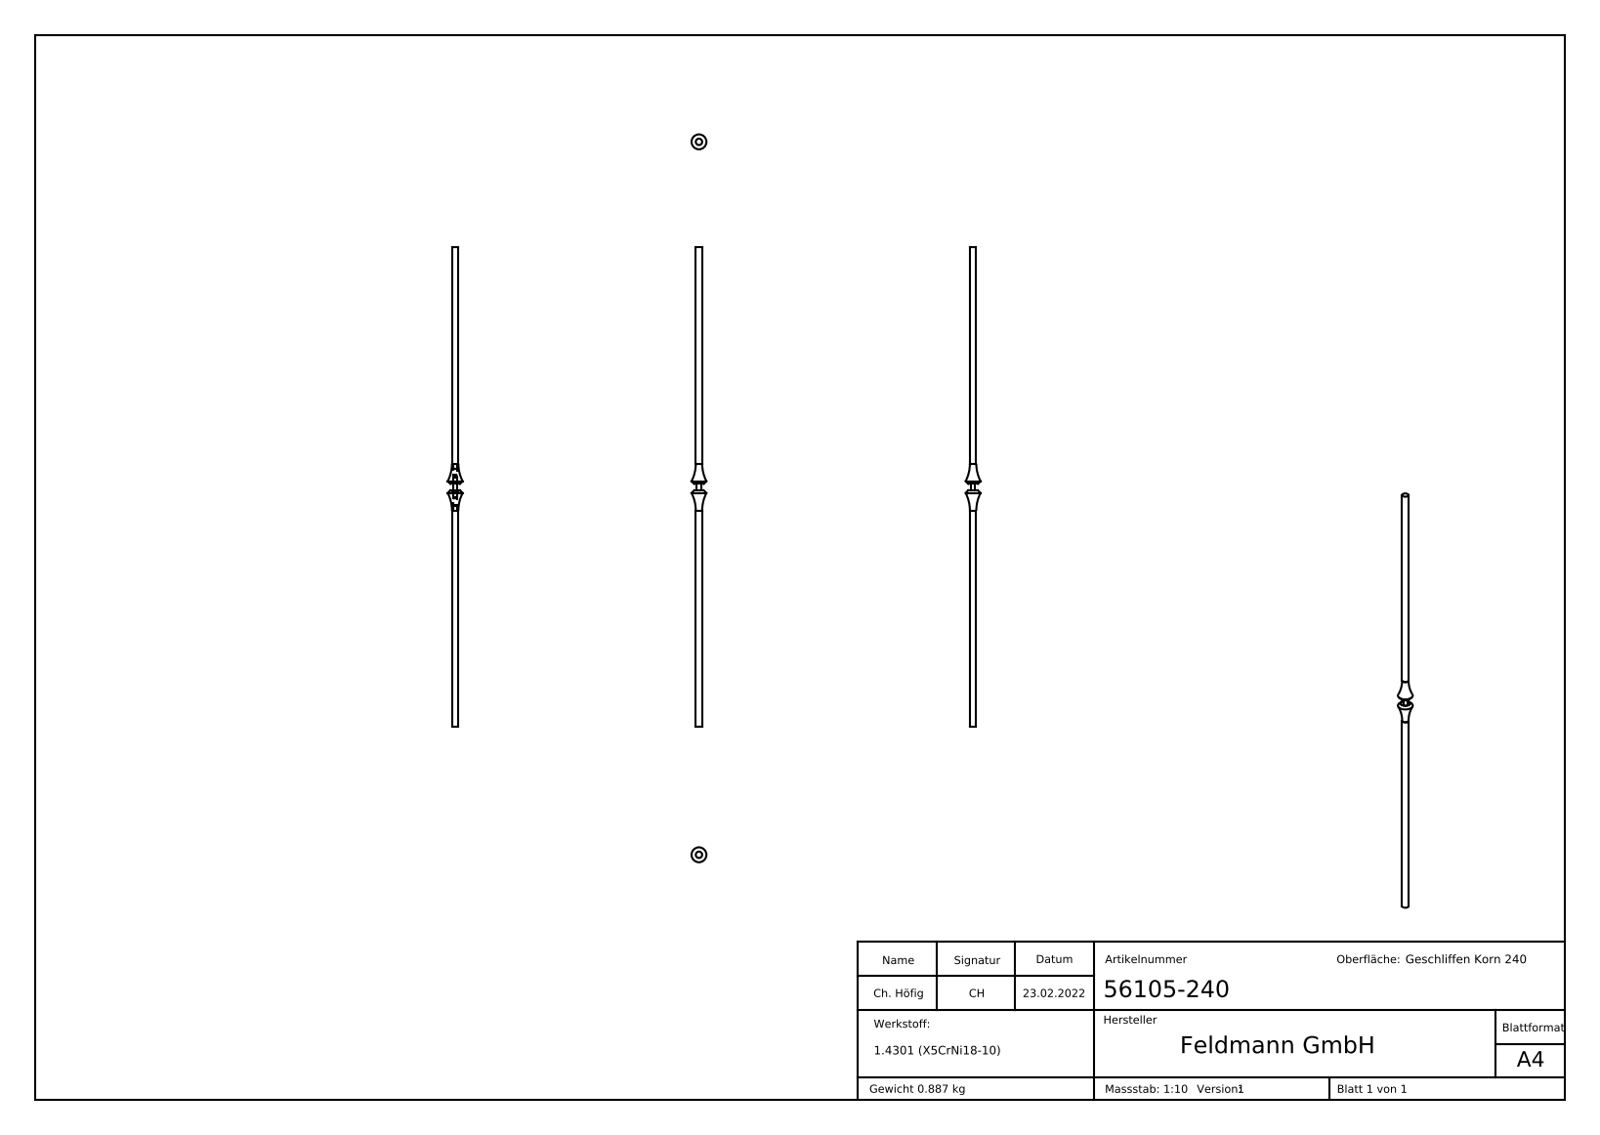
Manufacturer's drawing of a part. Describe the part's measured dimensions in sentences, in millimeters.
The part is named "56105-240 Teil1; 56105-240 Teil3; DIN914; 56105-240 (+3 more)". Its 3-D file was written by "SolidWorks 2018 (CONFIG_CONTROL_DESIGN)". It is 5 solids with 55 faces: 21 planar, 14 cylindrical and 20 other. Overall it measures 900 by 28 by 28 millimeters. Its volume is 112 323 cubic millimeters and its surface area 39 673 square millimeters. Round holes: 1 of diameter 6.8. Round bosses or shafts: 1 of diameter 12, 1 of diameter 8. The main face-to-face distances are 406, 494, 88, 900, 416, 484, 10, 78, 4, 11.5.
